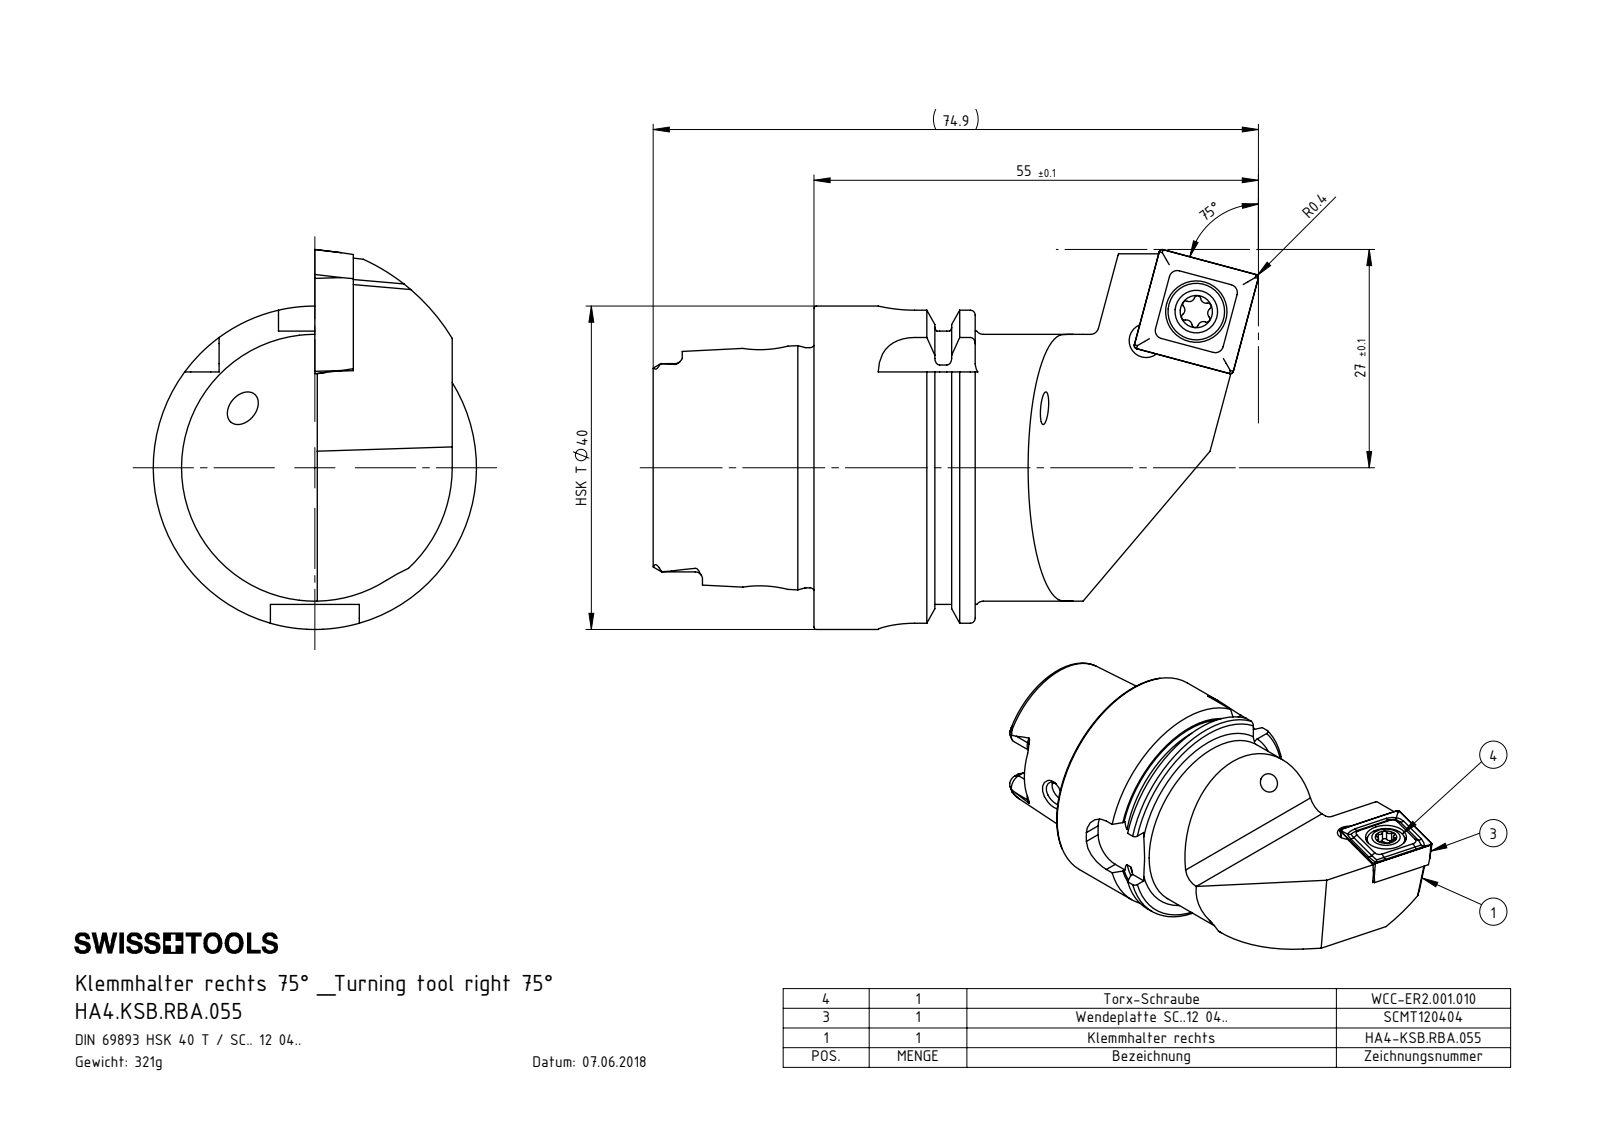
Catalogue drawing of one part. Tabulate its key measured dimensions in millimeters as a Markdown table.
| quantity | value |
| --- | --- |
| part name | WCC-ER2.001.010_A; HA4-KSB.RBA.055_A_Fertigbearbeitung; HA4.KSB.RBA.055; KVT_MB_600_040 (+1 more) |
| STEP written by | SolidWorks 2017 (AUTOMOTIVE_DESIGN) |
| units | millimeters |
| bodies | 5 solids, 306 faces (78 planar, 90 cylindrical, 138 other) |
| overall size | 74.9 × 47 × 40 |
| volume | 40 874 mm³ |
| surface area | 13 799 mm² |
| round holes (diameter × count) | 3.3 × 2, 4.2 × 2, 3 × 1, 4 × 1, 4.6 × 1, 5 × 1, 5.5 × 1, 7.6 × 1, 10 × 1, 11 × 1, 12.5 × 1, 21 × 1 |
| round bosses / shafts (diameter × count) | 40 × 1, 34.75 × 1, 33 × 1, 29.71 × 1, 7 × 1, 5 × 1, 4 × 1 |
| partial cylindrical surfaces (radius × count) | 0.39 × 6, 0.9 × 6, 1.88 × 4, 4.5 × 4, 0.69 × 3, 0.69 × 3, 3 × 1, 17 × 1 |
| main face-to-face distances | 4.46, 12.24, 16.7, 7.95, 19.95, 12, 19.9, 27.85, 39.85, 35.7 |
| hole center spacings | 7.07, 7.17, 37.55, 44.59, 44.7 |
